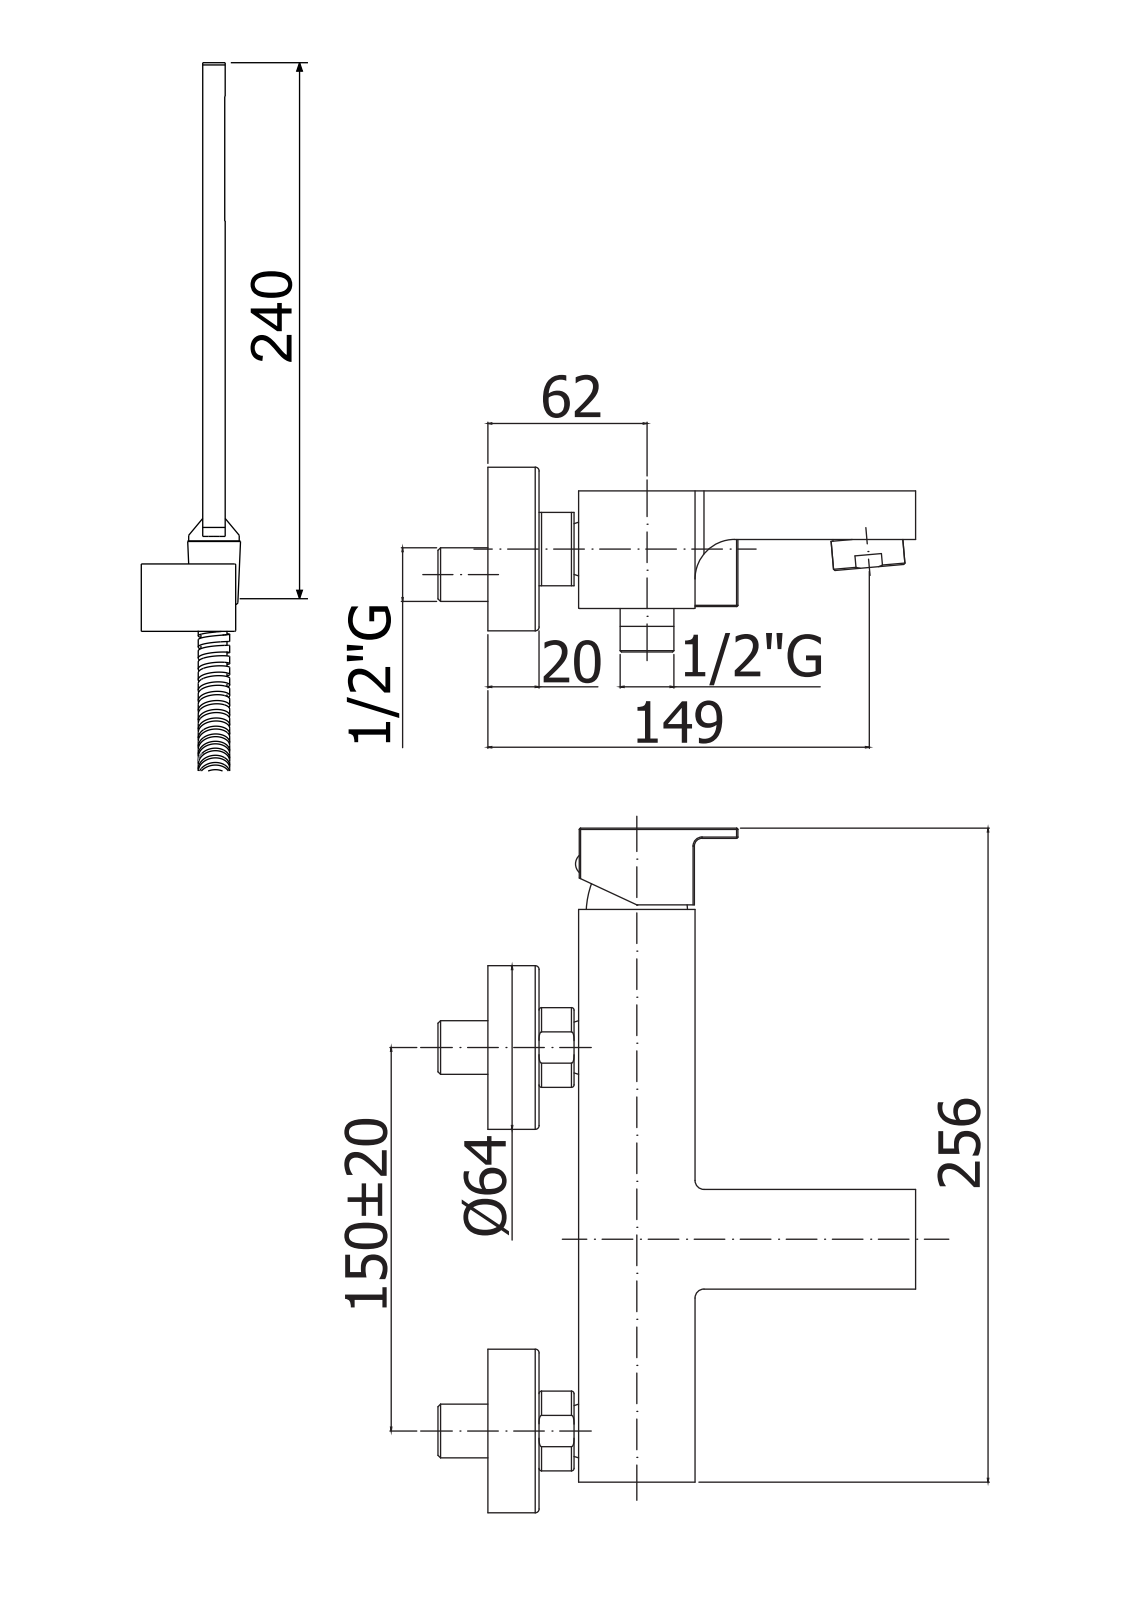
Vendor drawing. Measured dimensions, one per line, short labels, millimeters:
name: EF026CR
written by: CREO PARAMETRIC BY PTC INC, 2020044 (CONFIG_CONTROL_DESIGN)
unit: mm
bodies: 4 solids, 3360 faces (2531 planar, 484 cylindrical, 345 other)
size: 383.25 × 374.25 × 168.25
volume: 431 954 mm³; area: 253 578 mm²
holes: 4× ⌀7, 3× ⌀8.5, 3× ⌀24.5, 3× ⌀25, 2× ⌀4, 2× ⌀4.75, 2× ⌀10.5, 2× ⌀12.7, 2× ⌀18, 2× ⌀21, 2× ⌀21.6, 2× ⌀28.5
bosses: 11× ⌀2, 3× ⌀24, 2× ⌀63.5, 2× ⌀28, 2× ⌀27, 2× ⌀26.5, 2× ⌀17.7, 2× ⌀10
rounds: 57× R0.5, 18× R1, 11× R0.15, 8× R0.3, 7× R3, 3× R4, 2× R6.75, 2× R15.6
face distances: 3.75, 42.75, 46.5, 3, 39, 15.6, 8, 18, 10, 50.35
hole spacings: 7.07, 8.6, 11.4, 1.17, 4, 6, 6.21, 7.44
